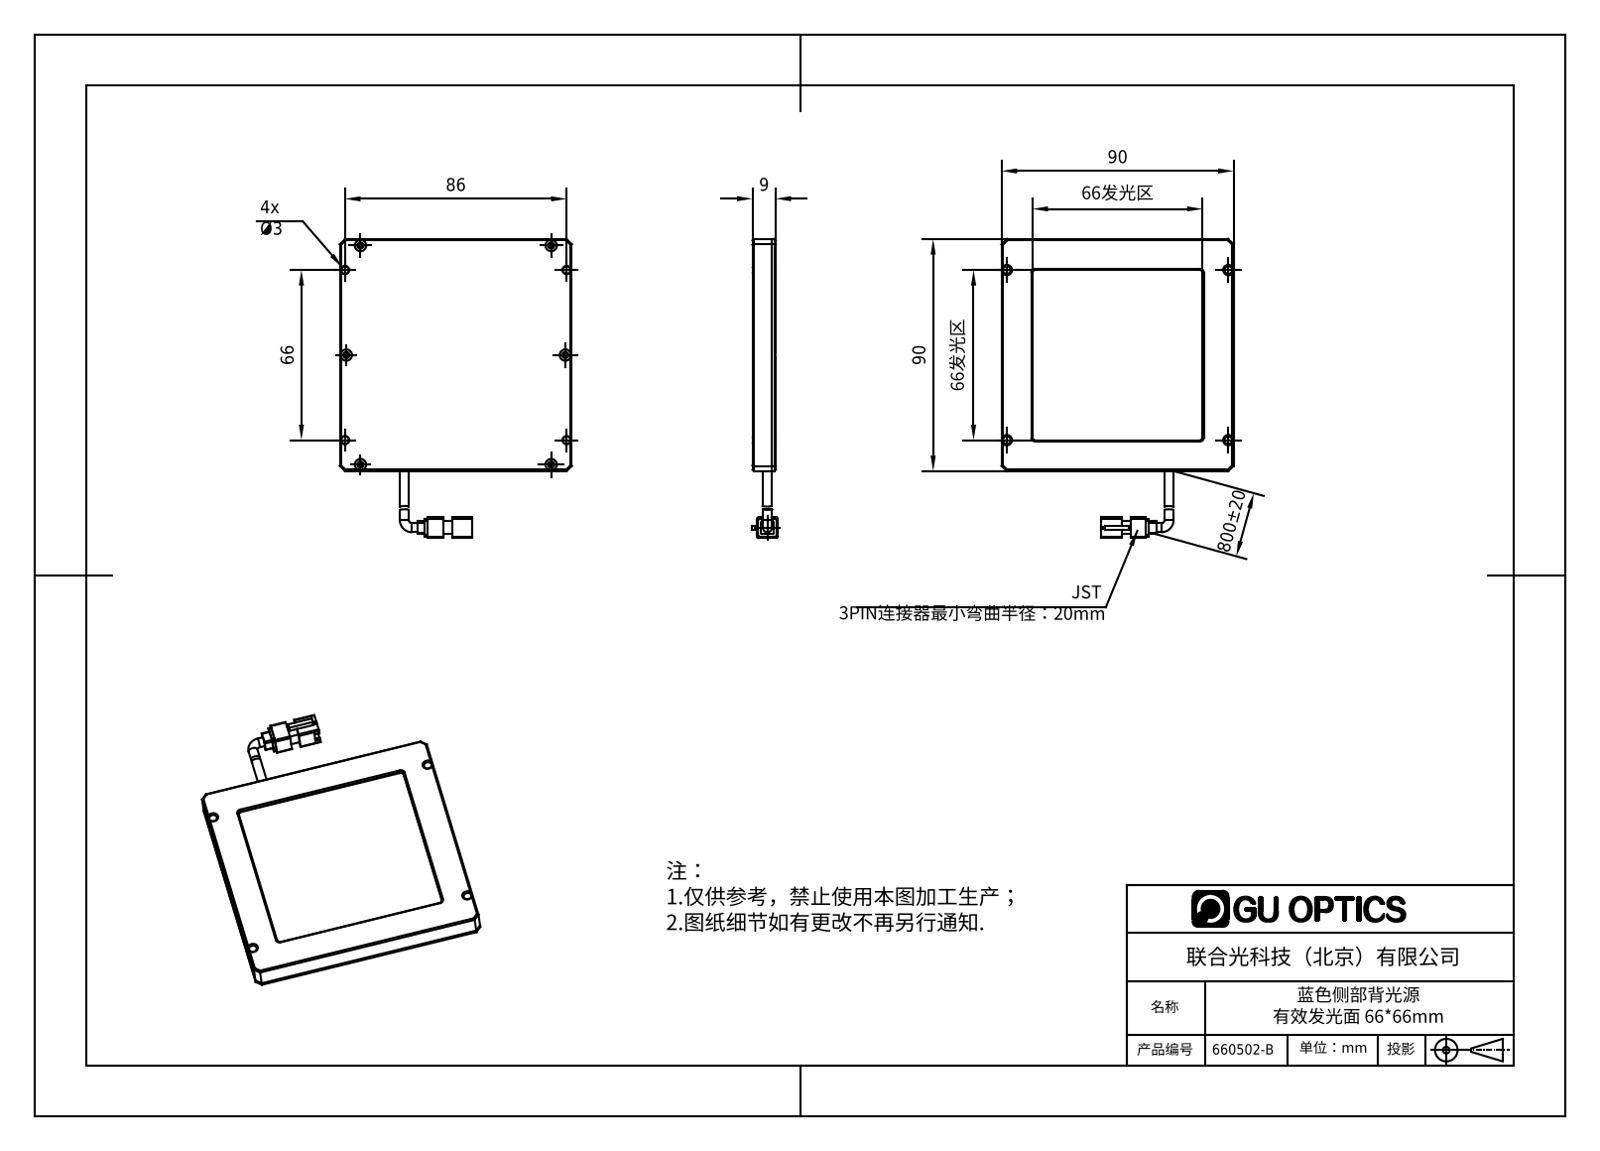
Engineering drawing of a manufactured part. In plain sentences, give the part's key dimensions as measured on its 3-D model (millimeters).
The part is named "660502-B". Its 3-D file was written by "SolidWorks 2016 (AUTOMOTIVE_DESIGN)". It is 6 solids with 417 faces: 242 planar, 76 cylindrical and 99 other. Overall it measures 116 by 90 by 10 millimeters. Its volume is 46 033 cubic millimeters and its surface area 43 334 square millimeters. Round holes: 6 of diameter 1.6, 6 of diameter 2.4, 4 of diameter 3, 4 of diameter 3.2. Round bosses or shafts: 2 of diameter 3.5. Partial cylindrical surfaces (rounded edges, fillets, slot ends): 10 of radius 1, 8 of radius 0.5, 4 of radius 2, 1 of radius 1.6. The main face-to-face distances are 4, 8, 1.5, 6.5, 2.5, 5, 9, 1, 7.5, 86. The hole center spacings are 11.24, 33, 42.85, 75.74, 80.56, 90.15, 91.65, 110.
